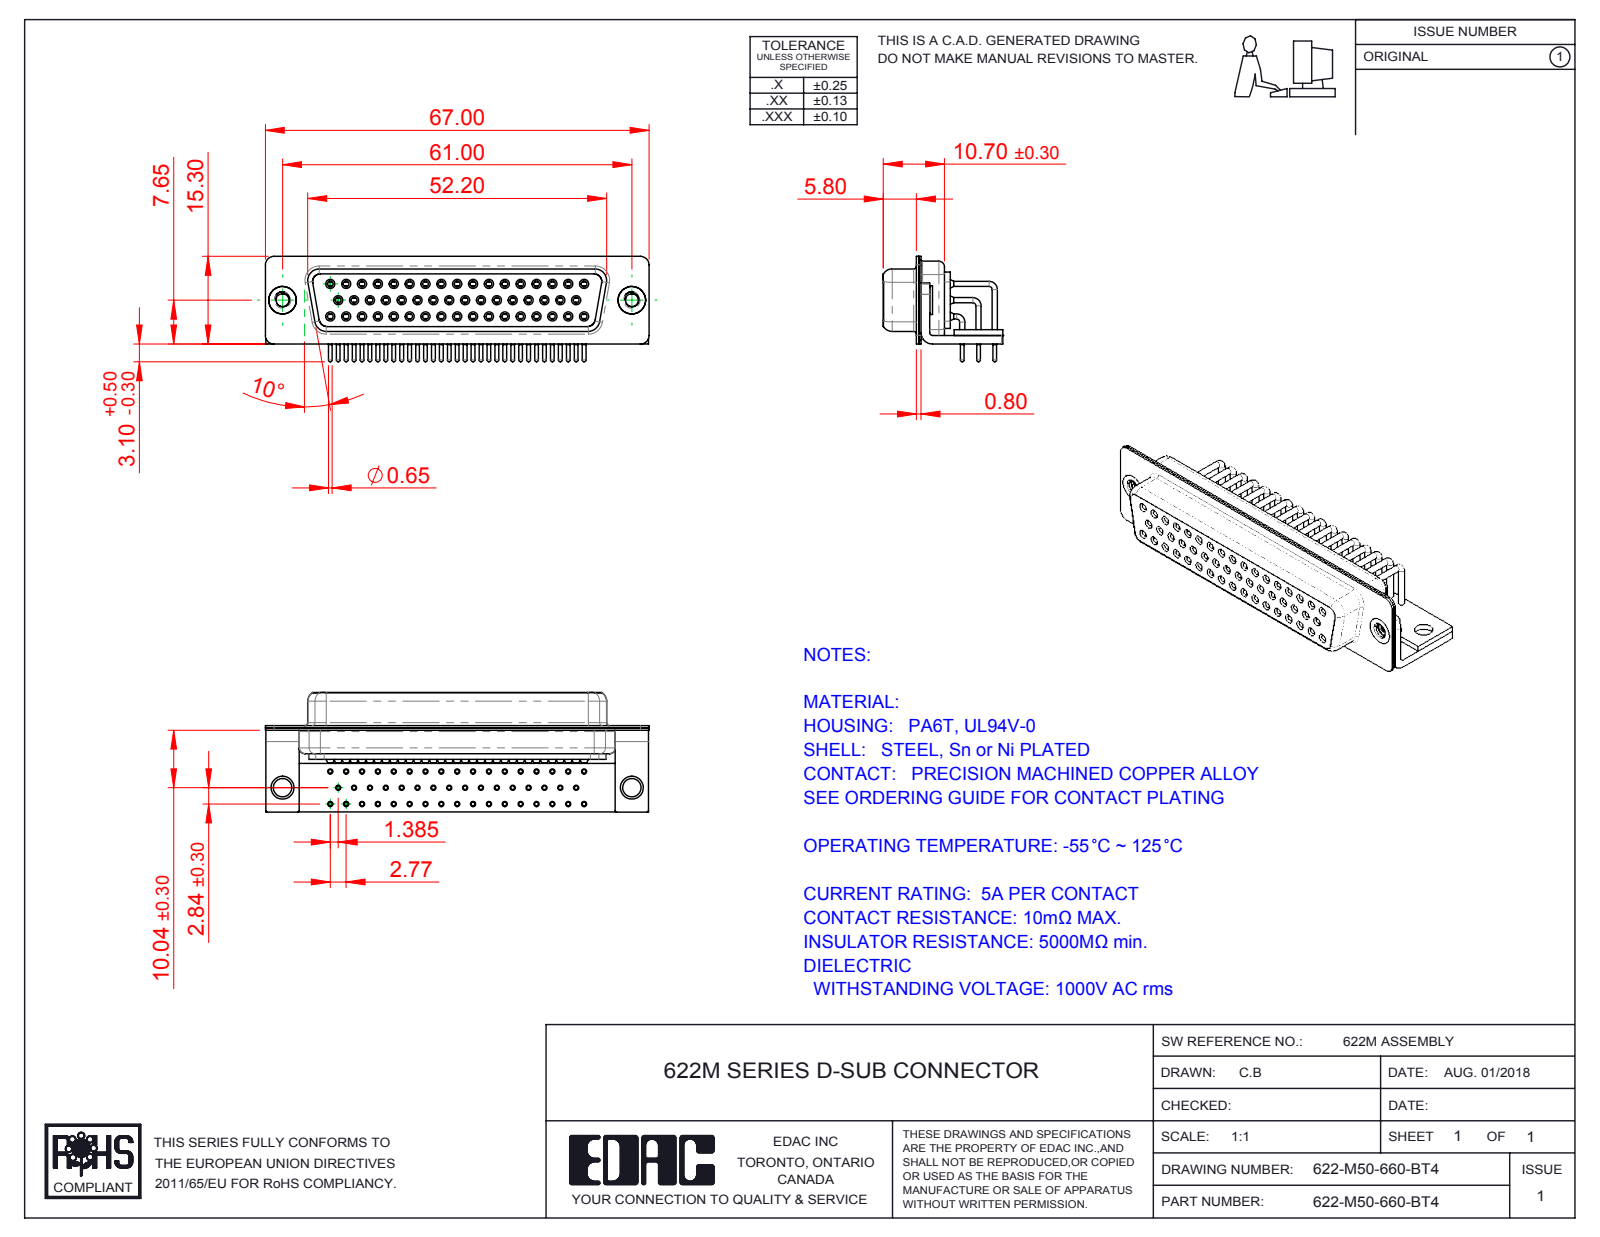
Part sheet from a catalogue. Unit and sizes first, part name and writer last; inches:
Units: inches
Overall size (bounding box): 2.638 × 0.823 × 0.724
Round holes (diameter × count): ⌀0.035 ×50, ⌀0.039 ×50, ⌀0.043 ×50, ⌀0.067 ×50, ⌀0.071 ×50, ⌀0.079 ×50, ⌀0.089 ×2, ⌀0.126 ×2, ⌀0.157 ×2, ⌀0.189 ×2
Round bosses / shafts (diameter × count): ⌀0.035 ×59, ⌀0.063 ×50, ⌀0.059 ×50, ⌀0.026 ×50, ⌀0.197 ×2, ⌀0.193 ×2
Partial cylindrical surfaces — rounded edges, fillets, slot ends (radius × count): R0.01 ×16, R0.059 ×16, R0.079 ×13, R0.053 ×8, R0.063 ×8, R0.02 ×5, R0.024 ×4, R0.026 ×4
Main face-to-face distances: 0.016, 0.039, 0.087, 0.033, 0.053, 0.467, 0.482, 0.228, 0.232, 0.031
Hole centre spacings: 0.109, 0.124, 0.218, 0.327, 0.436, 0.545, 0.654, 0.763
Volume: 0.473 in³ · Surface area: 28.08 in²
Bodies: 58 solids, 3079 faces (843 planar, 1409 cylindrical, 827 other)
Part name (STEP PRODUCT): 622M Contact Row 2_50 Contacts; 622M Contact Row 1_50 Contacts; 622M Shell Front_50 Contacts; 622-M50-660-BT4 (+6 more)
STEP written by: SolidWorks 2016 (CONFIG_CONTROL_DESIGN)
